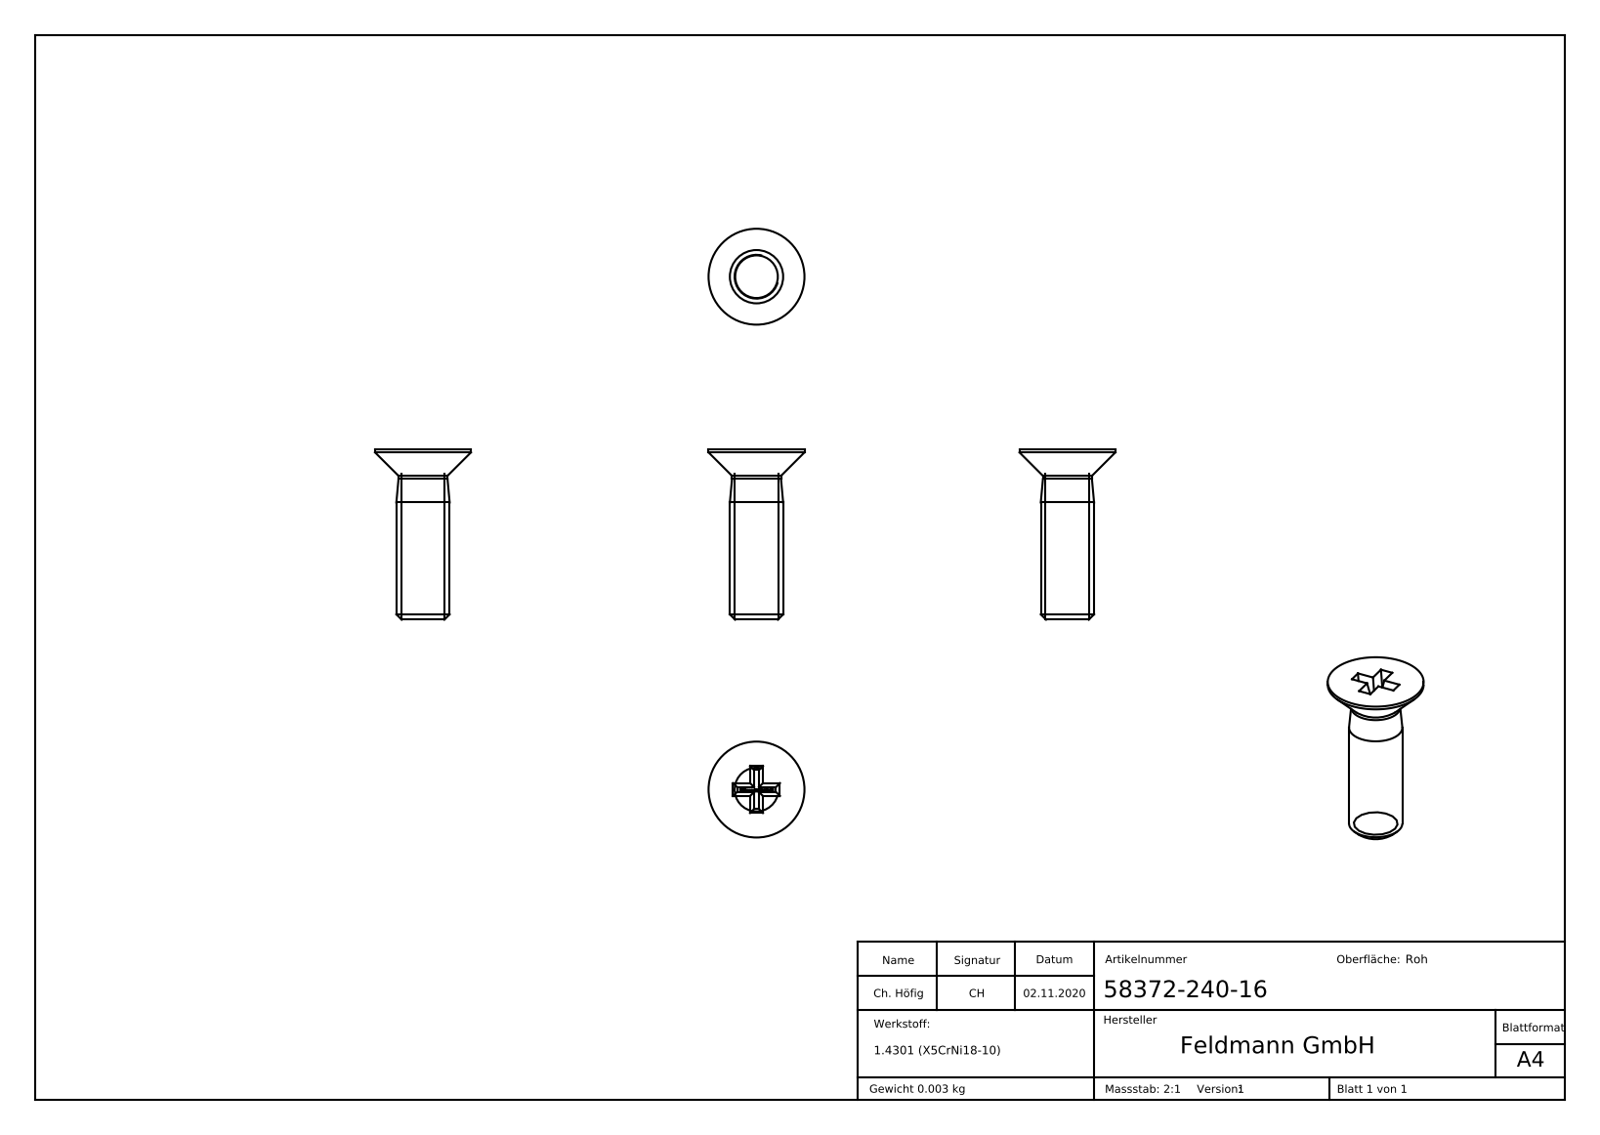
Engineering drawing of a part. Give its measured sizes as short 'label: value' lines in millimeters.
name: 58372-240-16
written by: SolidWorks 2018 (CONFIG_CONTROL_DESIGN)
unit: mm
bodies: 1 solid, 283 faces (154 planar, 6 cylindrical, 123 other)
size: 16 × 9 × 9
volume: 348 mm³; area: 394 mm²
bosses: 1× ⌀9, 1× ⌀5, 1× ⌀4.6
face distances: 16, 1.57, 13.9, 2.1, 13.8, 2.2, 0.36, 2.57, 0.31, 0.5
